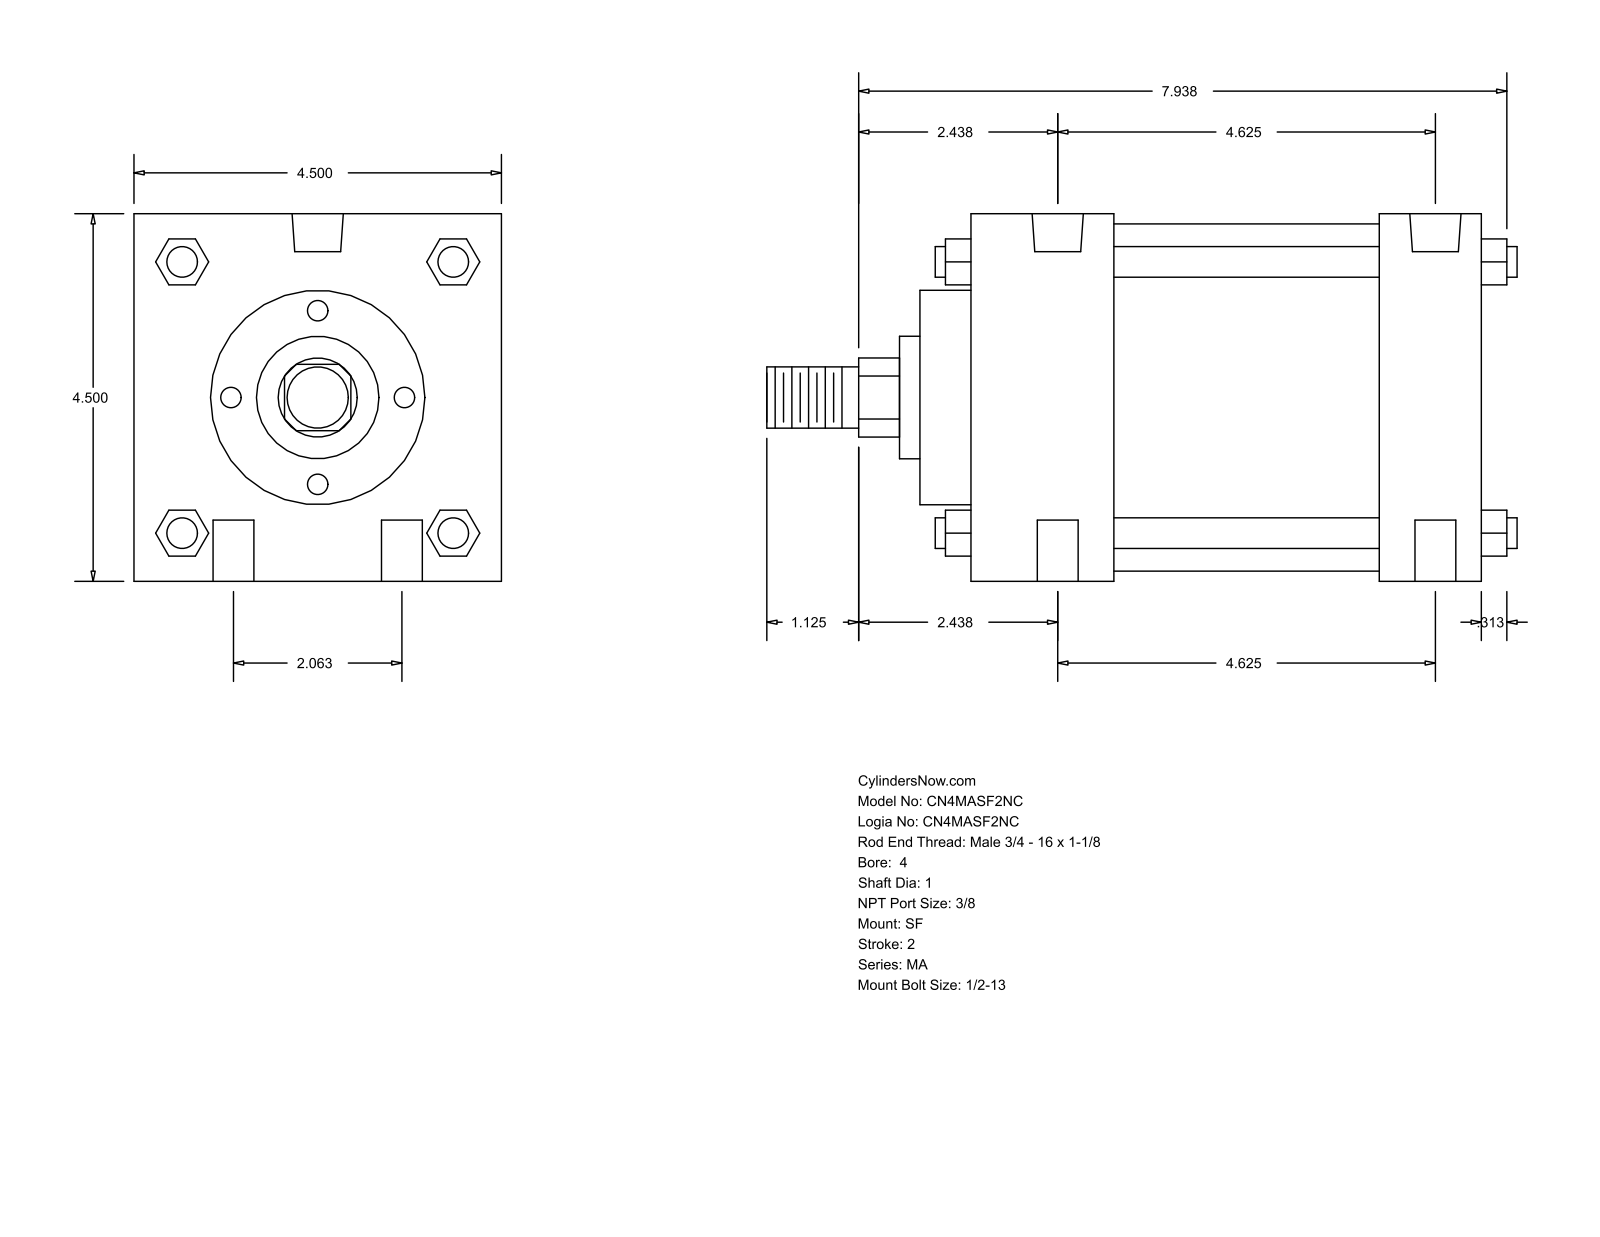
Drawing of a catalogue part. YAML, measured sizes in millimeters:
part_name: "MA_SF__0400_1"
step_written_by: "GSSL Pune (CONFIG_CONTROL_DESIGN)"
units: millimeters
bodies: {solids: 0, faces: 126, planar: 95, cylindrical: 31, other: 0}
overall_size: [233.36, 114.3, 114.3]
round_holes:
  - {diameter: 12.7, count: 4}
  - {diameter: 11.11, count: 2}
  - {diameter: 15.93, count: 2}
round_bosses_or_shafts:
  - {diameter: 9.53, count: 4}
  - {diameter: 107.95, count: 1}
  - {diameter: 66.67, count: 1}
  - {diameter: 38.1, count: 1}
  - {diameter: 25.4, count: 1}
  - {diameter: 19.05, count: 1}
partial_cylinders:
  - {radius: 12.29, count: 1}
face_to_face_distances: [114.3, 158.76, 127.01, 31.75, 44.46, 82.55, 15.87, 60.33, 142.88, 174.63]
hole_center_spacings: [26.19, 120.36, 117.48, 52.38, 128.63, 107.95]
